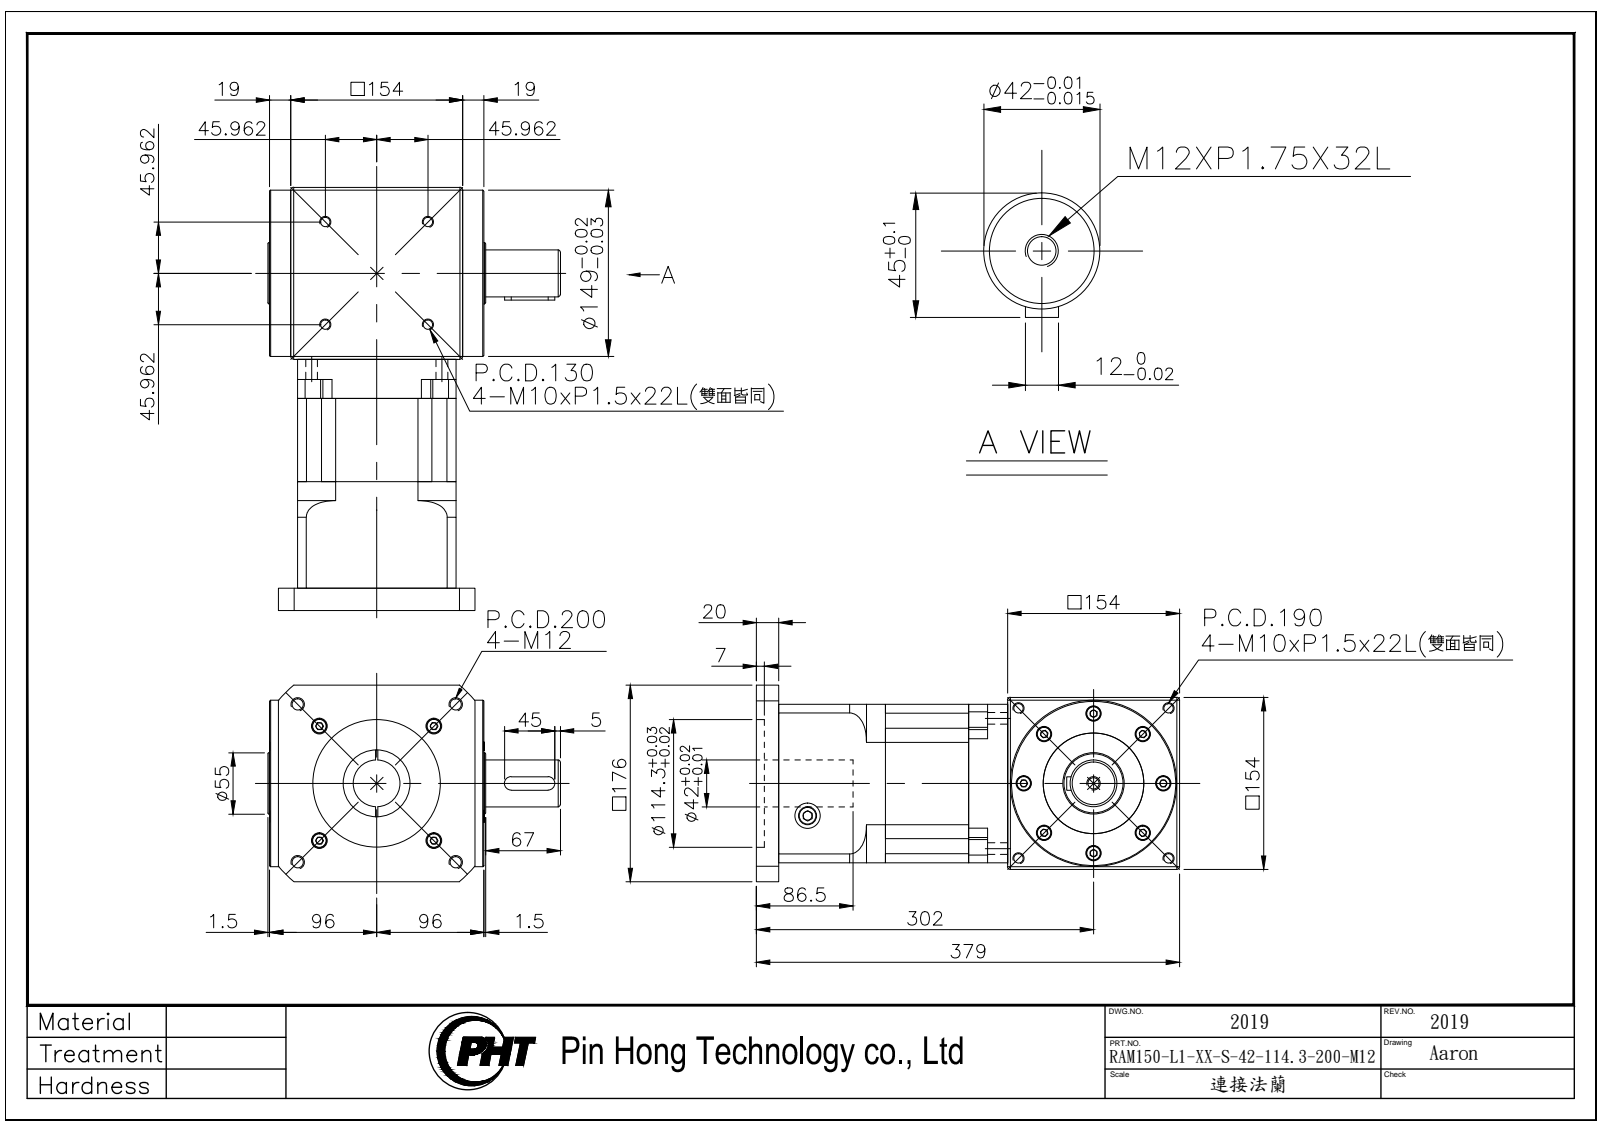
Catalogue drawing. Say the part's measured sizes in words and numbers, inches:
The part is named "RAM150-L2-XX-S-42-114.3-200-M12_2019". Its 3-D file was written by "SolidWorks 2016 (AUTOMOTIVE_DESIGN)". It is 5 solids with 893 faces: 416 planar, 317 cylindrical and 160 other. Overall it measures 14.921 by 10.315 by 6.929 inches. Its volume is 511.5 cubic inches and its surface area 892.8 square inches. Round holes: 12 of diameter 0.335, 12 of diameter 0.354, 12 of diameter 0.551, 8 of diameter 0.433, 8 of diameter 0.689, 5 of diameter 0.402, 4 of diameter 0.268, 4 of diameter 0.413, 2 of diameter 0.886, 1 of diameter 0.161, 1 of diameter 1.654, 1 of diameter 2.362. Round bosses or shafts: 12 of diameter 0.63, 4 of diameter 0.512, 1 of diameter 5.866, 1 of diameter 5.118, 1 of diameter 3.543, 1 of diameter 2.913, 1 of diameter 2.165, 1 of diameter 1.654. Partial cylindrical surfaces (rounded edges, fillets, slot ends): 4 of radius 0.394, 2 of radius 0.236, 1 of radius 3.15, 1 of radius 3.74, 1 of radius 4.228, 1 of radius 4.528. The main face-to-face distances are 0.236, 5.827, 6.063, 5.591, 2.933, 4.311, 1.378, 0.984, 10.374, 7.441. The hole center spacings are 2.795, 0.737, 0.74, 0.908, 1.433, 1.883, 2.651, 3.265.
